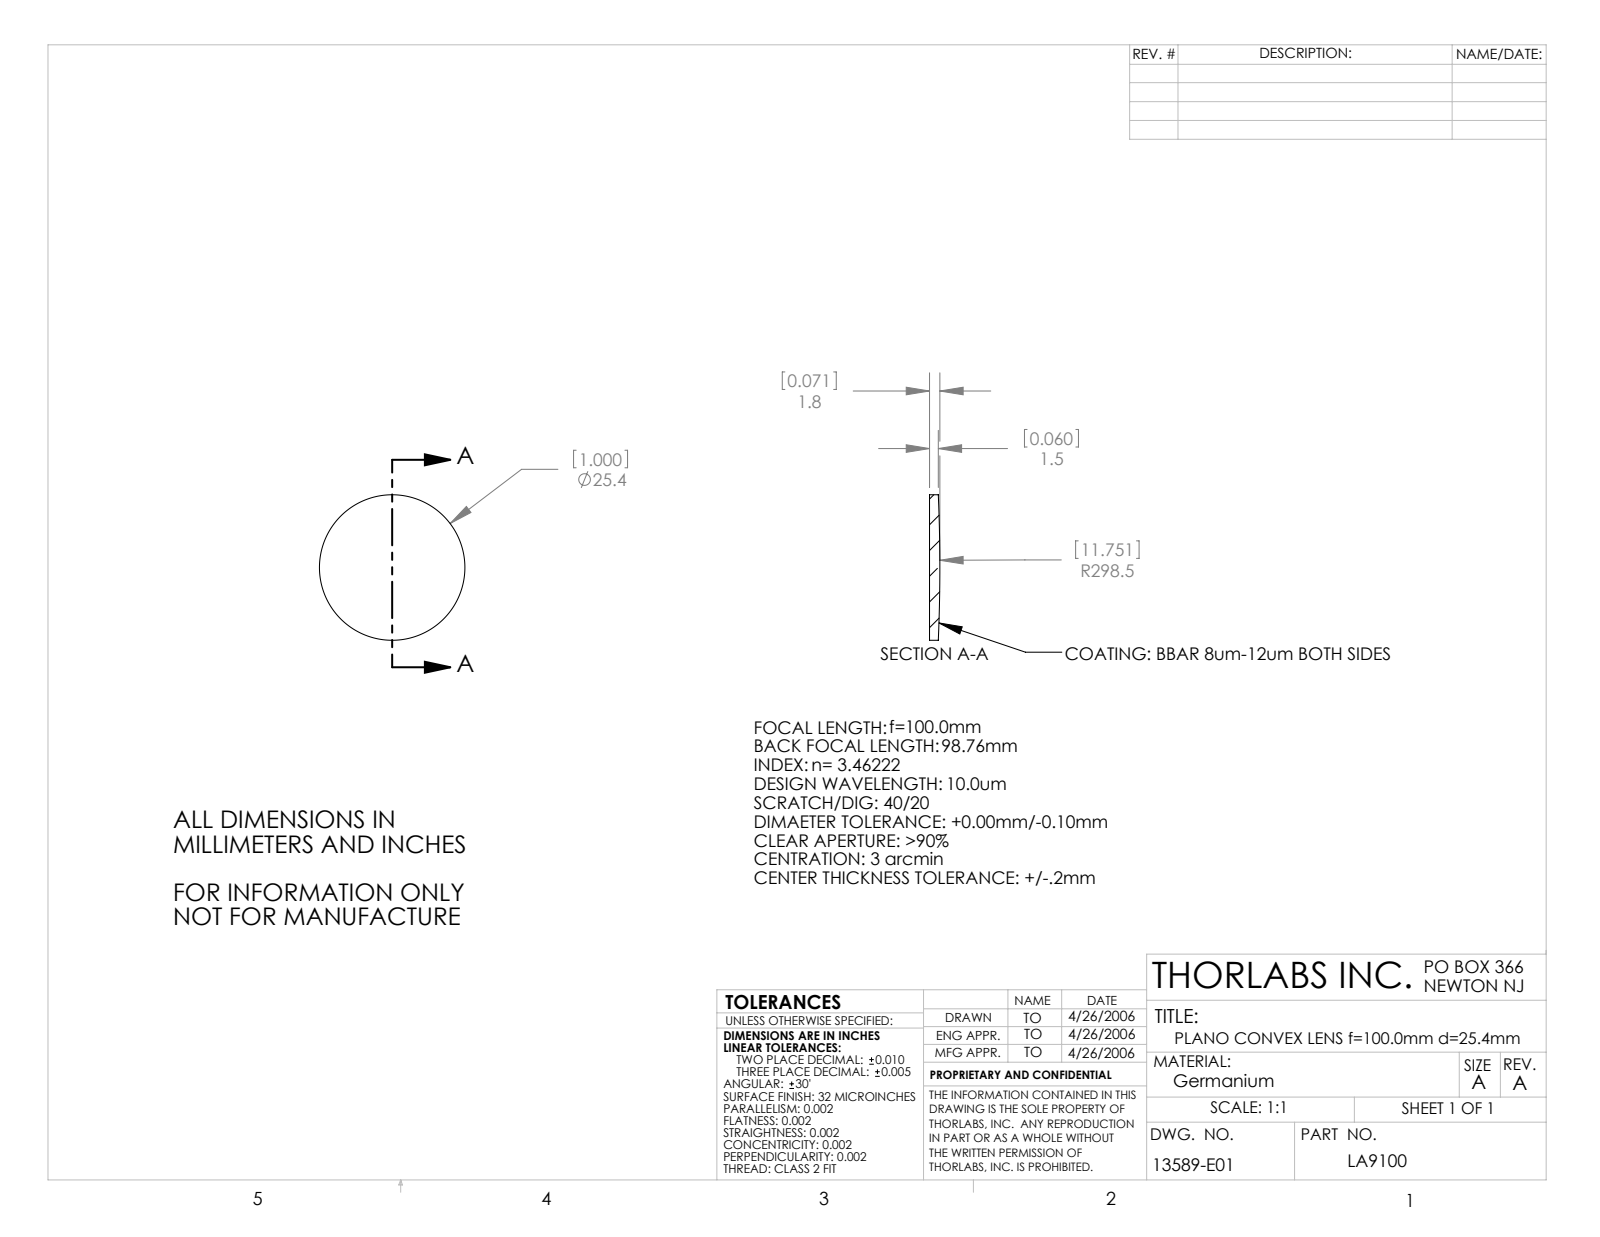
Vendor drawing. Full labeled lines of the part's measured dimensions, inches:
Part name (STEP PRODUCT): 13589-E0W
STEP written by: SolidWorks 2007 (AUTOMOTIVE_DESIGN)
Units: inches
Bodies: 0 solids, 5 faces (1 planar, 2 cylindrical, 2 other)
Overall size (bounding box): 1 × 1 × 0.071
Round bosses / shafts (diameter × count): ⌀1 ×1
